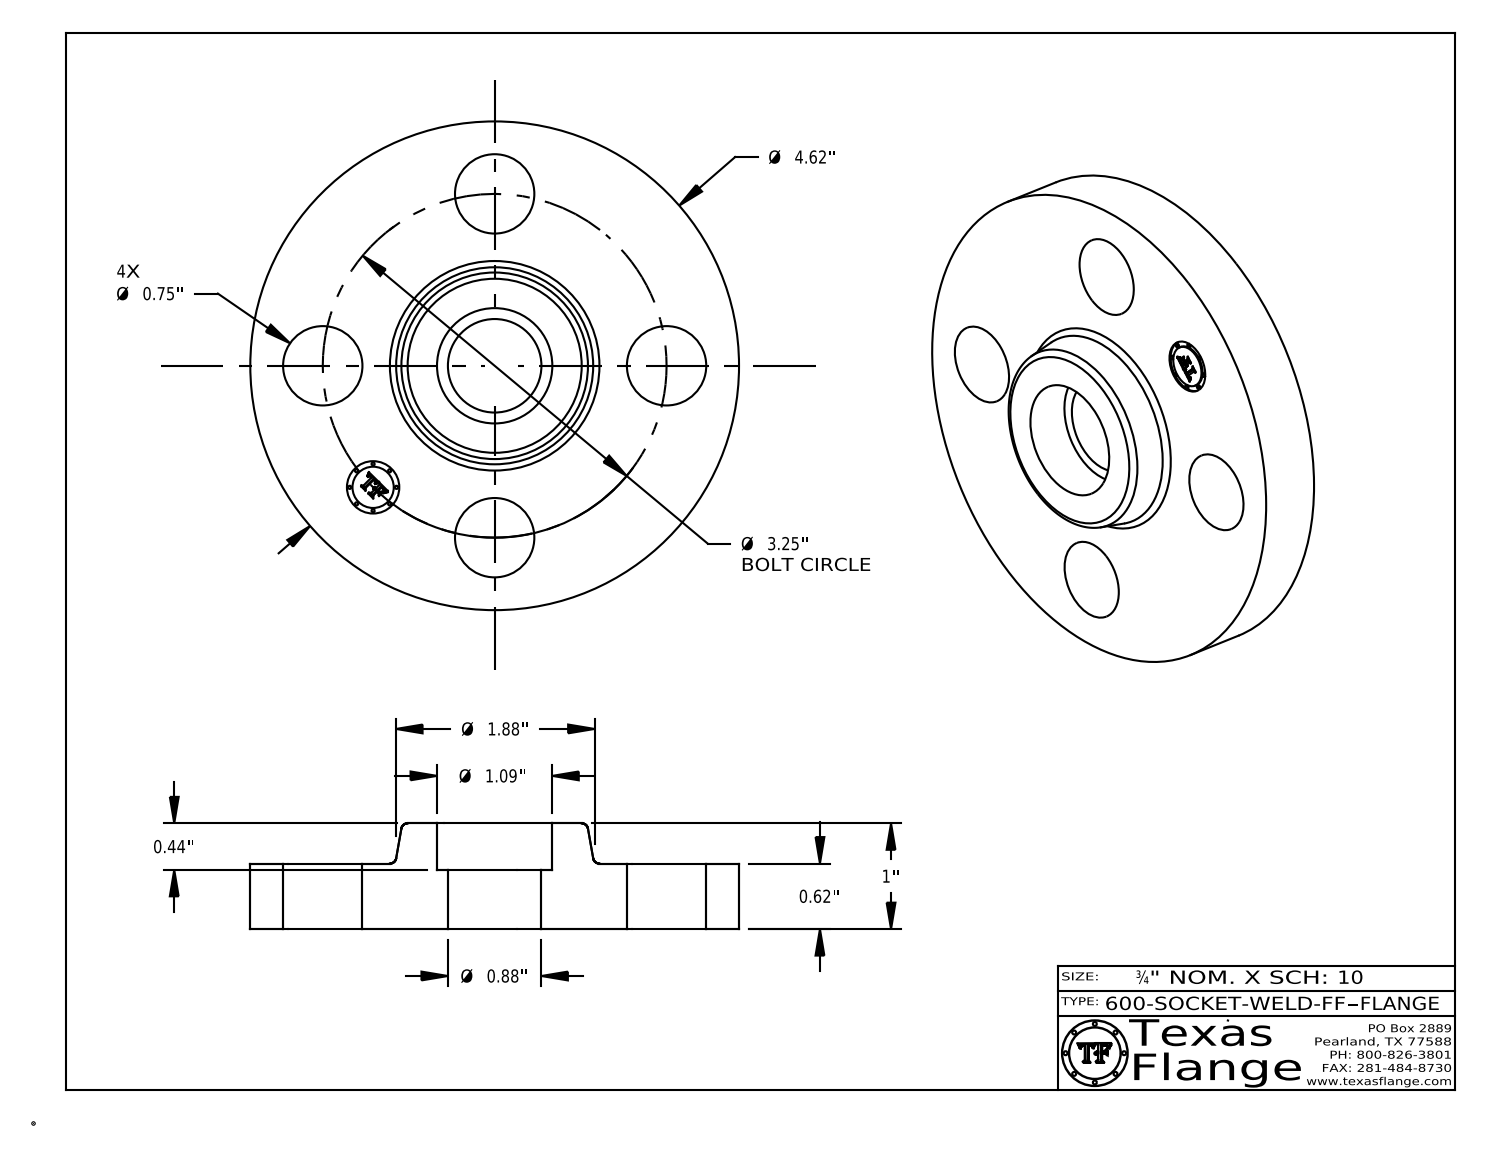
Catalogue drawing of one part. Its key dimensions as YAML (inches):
part_name: "600-SOCKET-WELD-FF"
step_written_by: "CATIA V5 STEP AP214 (AUTOMOTIVE_DESIGN)"
units: inches
bodies: {solids: 1, faces: 409, planar: 369, cylindrical: 34, other: 6}
overall_size: [4.62, 4.62, 1]
volume: 9.524
surface_area: 48.39
round_holes:
  - {diameter: 0.75, count: 4}
  - {diameter: 0.495, count: 1}
  - {diameter: 0.884, count: 1}
  - {diameter: 1.09, count: 1}
round_bosses_or_shafts:
  - {diameter: 0.03, count: 8}
  - {diameter: 4.62, count: 1}
  - {diameter: 0.39, count: 1}
face_to_face_distances: [0.62, 1, 0.38, 0.56, 0.06, 0.44, 0.605, 0.045, 0.015, 0.395]
hole_center_spacings: [1.625, 2.298, 1.244, 3.003, 3.25]
